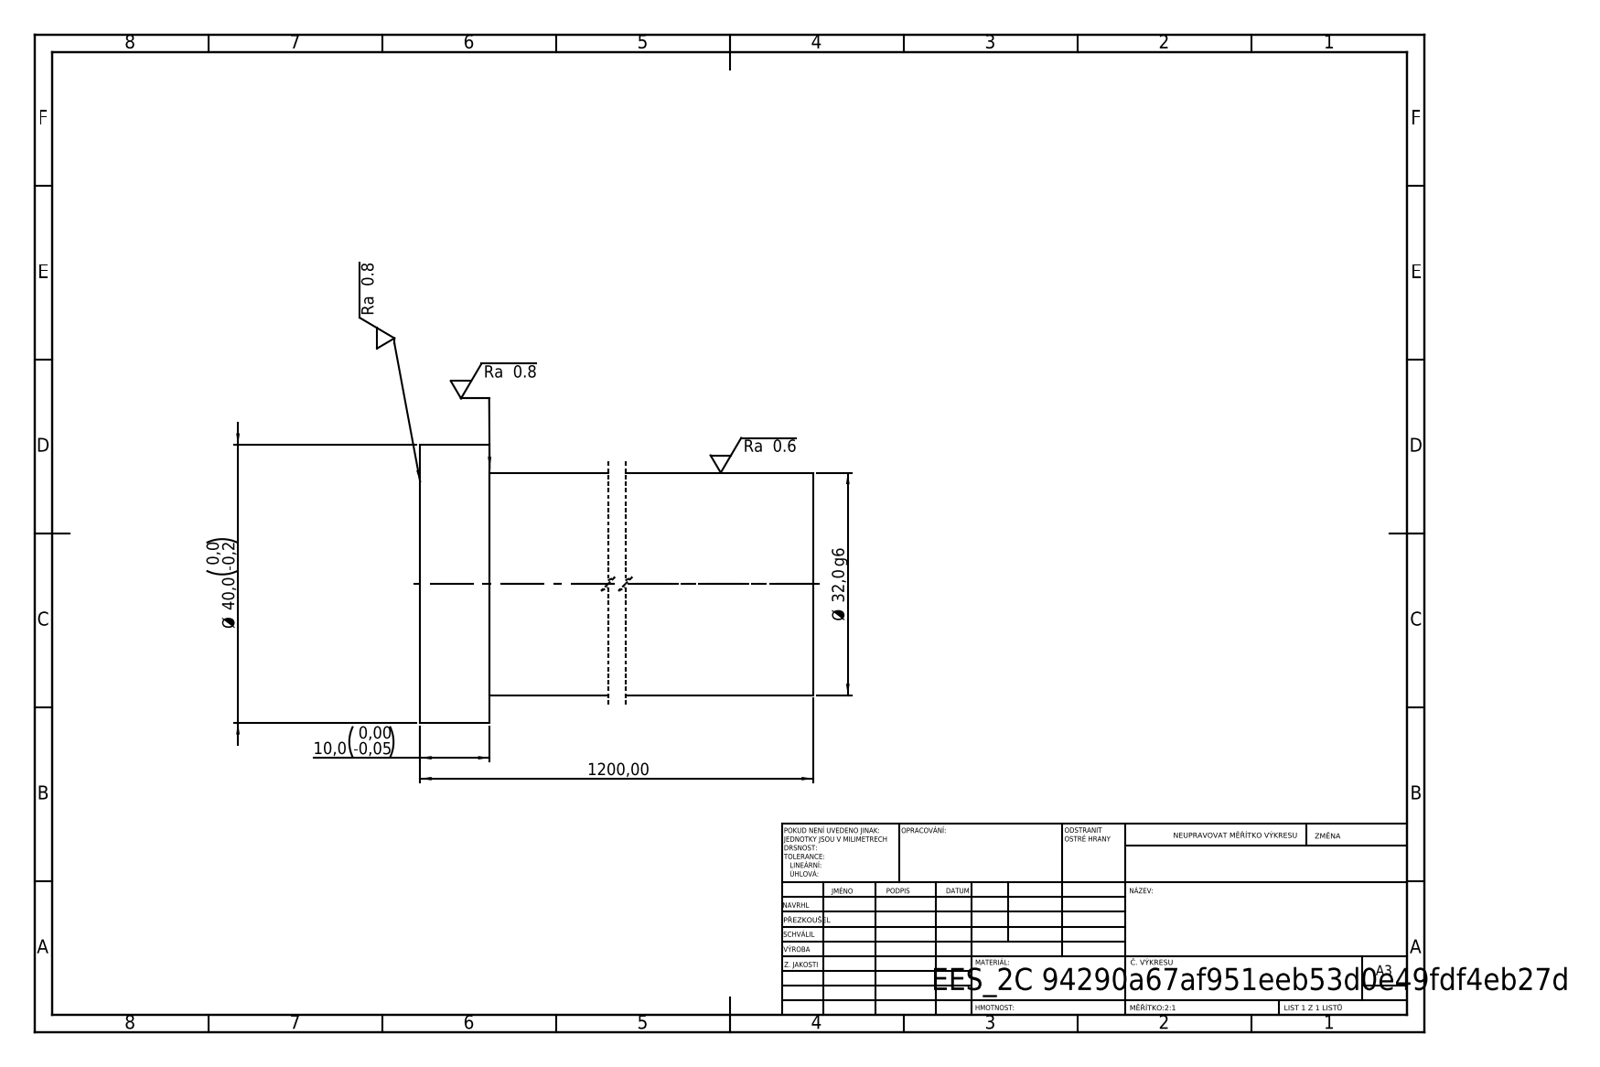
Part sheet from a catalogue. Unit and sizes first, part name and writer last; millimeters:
Units: millimetres
Overall size (bounding box): 1200 × 40 × 40
Round bosses / shafts (diameter × count): ⌀40 ×1, ⌀32 ×1
Main face-to-face distances: 1200, 10, 1190
Volume: 969 621 mm³ · Surface area: 123 402 mm²
Bodies: 1 solid, 7 faces (3 planar, 4 cylindrical, 0 other)
STEP written by: SolidWorks 2019 (CONFIG_CONTROL_DESIGN)
